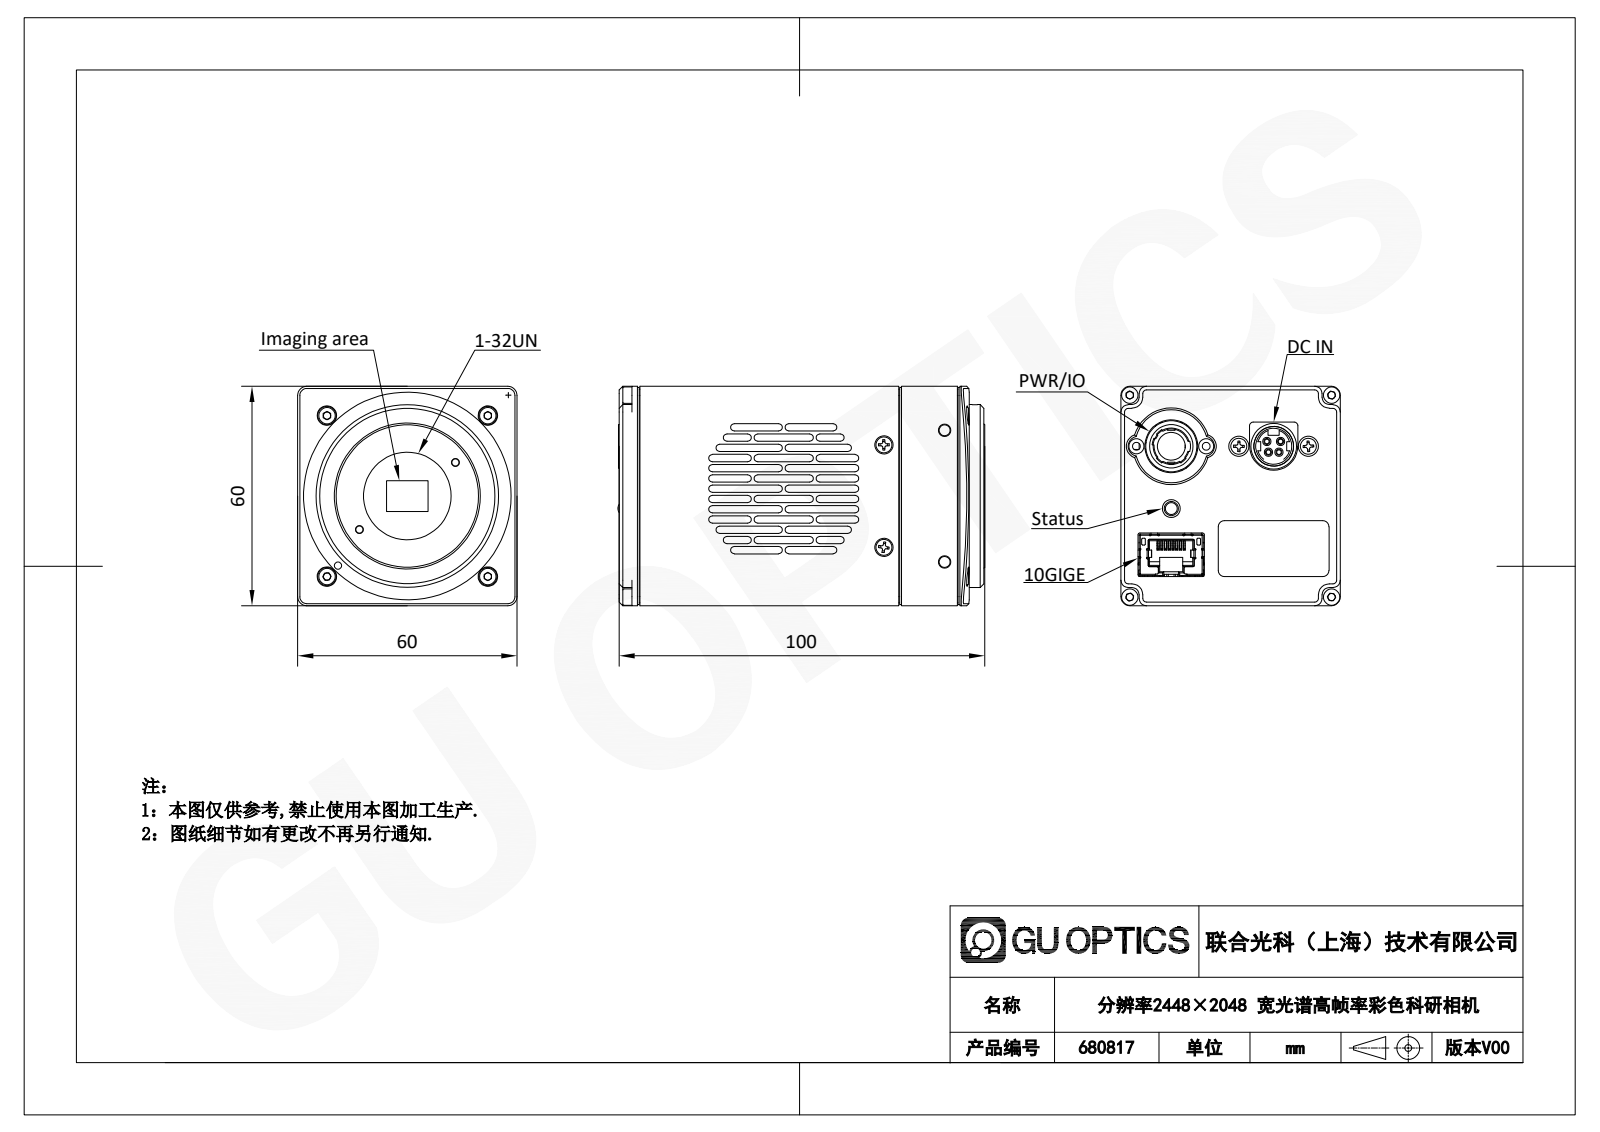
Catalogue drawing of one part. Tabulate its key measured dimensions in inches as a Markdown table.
| quantity | value |
| --- | --- |
| part name | cross recessed countersunk head screws gb2_GB_CROSS_SCREWS_TYPE10 M2.5X5-3.5-H1-N_1; 3405 PKG; KPJX-PM-4S_3-1-SOLID1_1; HR10A-10R-12PB(71)_1 (+8 more) |
| STEP written by | SolidWorks 2024 (CONFIG_CONTROL_DESIGN) |
| units | inches |
| bodies | 33 solids, 5790 faces (4320 planar, 1205 cylindrical, 265 other) |
| overall size | 3.949 × 2.362 × 2.362 |
| volume | 4.584 in³ |
| surface area | 137.9 in² |
| round holes (diameter × count) | 0.028 × 25, 0.106 × 14, 0.081 × 8, 0.087 × 8, 0.197 × 8, 0.063 × 7, 0.053 × 4, 0.067 × 4, 0.118 × 4, 0.079 × 3, 0.031 × 2, 0.037 × 2 |
| round bosses / shafts (diameter × count) | 0.024 × 178, 0.098 × 13, 0.177 × 8, 0.173 × 4, 0.063 × 3, 0.057 × 2, 0.039 × 2, 0.028 × 2 |
| partial cylindrical surfaces (radius × count) | 0.039 × 86, 0.012 × 83, 0.008 × 79, 0.079 × 40, 0.016 × 22, 0.01 × 21, 0.02 × 20, 0.059 × 20 |
| main face-to-face distances | 0.059, 2.303, 2.362, 2.244, 0.079, 0.157, 0.02, 3.611, 0.039, 0.177 |
| hole center spacings | 0.066, 0.1, 0.156, 0.2, 0.057, 1.896, 1.965, 2.111 |
